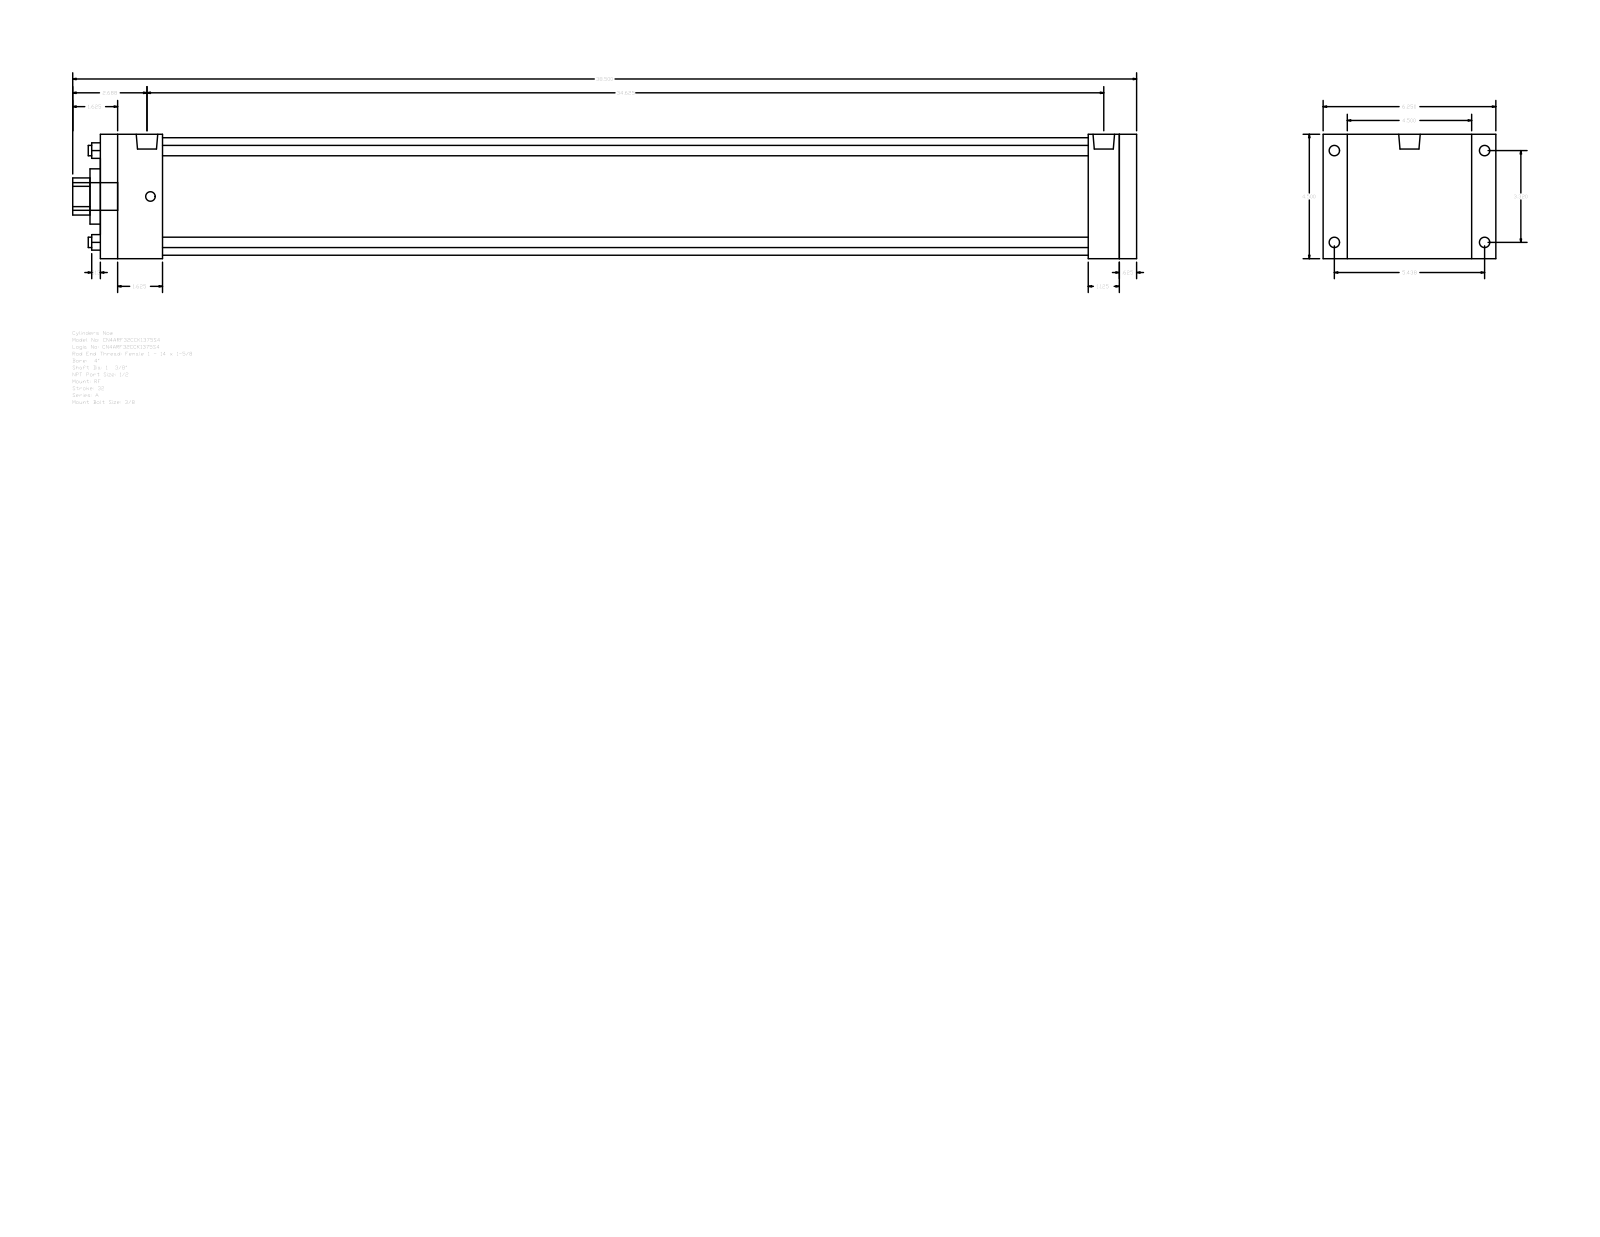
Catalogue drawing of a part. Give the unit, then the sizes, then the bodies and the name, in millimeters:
Units: millimetres
Overall size (bounding box): 977.9 × 158.75 × 114.3
Round holes (diameter × count): ⌀9.53 ×4, ⌀34.92 ×1, ⌀50.8 ×1, ⌀107.95 ×1
Round bosses / shafts (diameter × count): ⌀9.53 ×4, ⌀8.73 ×4, ⌀19.77 ×2, ⌀25.4 ×1
Partial cylindrical surfaces — rounded edges, fillets, slot ends (radius × count): R17.06 ×1
Main face-to-face distances: 114.3, 952.5, 15.88, 936.62, 28.57, 22.23, 136.53, 908.05, 44.45, 57.15
Hole centre spacings: 59.62, 84.32, 119.25
Bodies: 0 solids, 92 faces (64 planar, 28 cylindrical, 0 other)
Part name (STEP PRODUCT): A_RF__0400_1.375
STEP written by: GSSL Pune (CONFIG_CONTROL_DESIGN)
